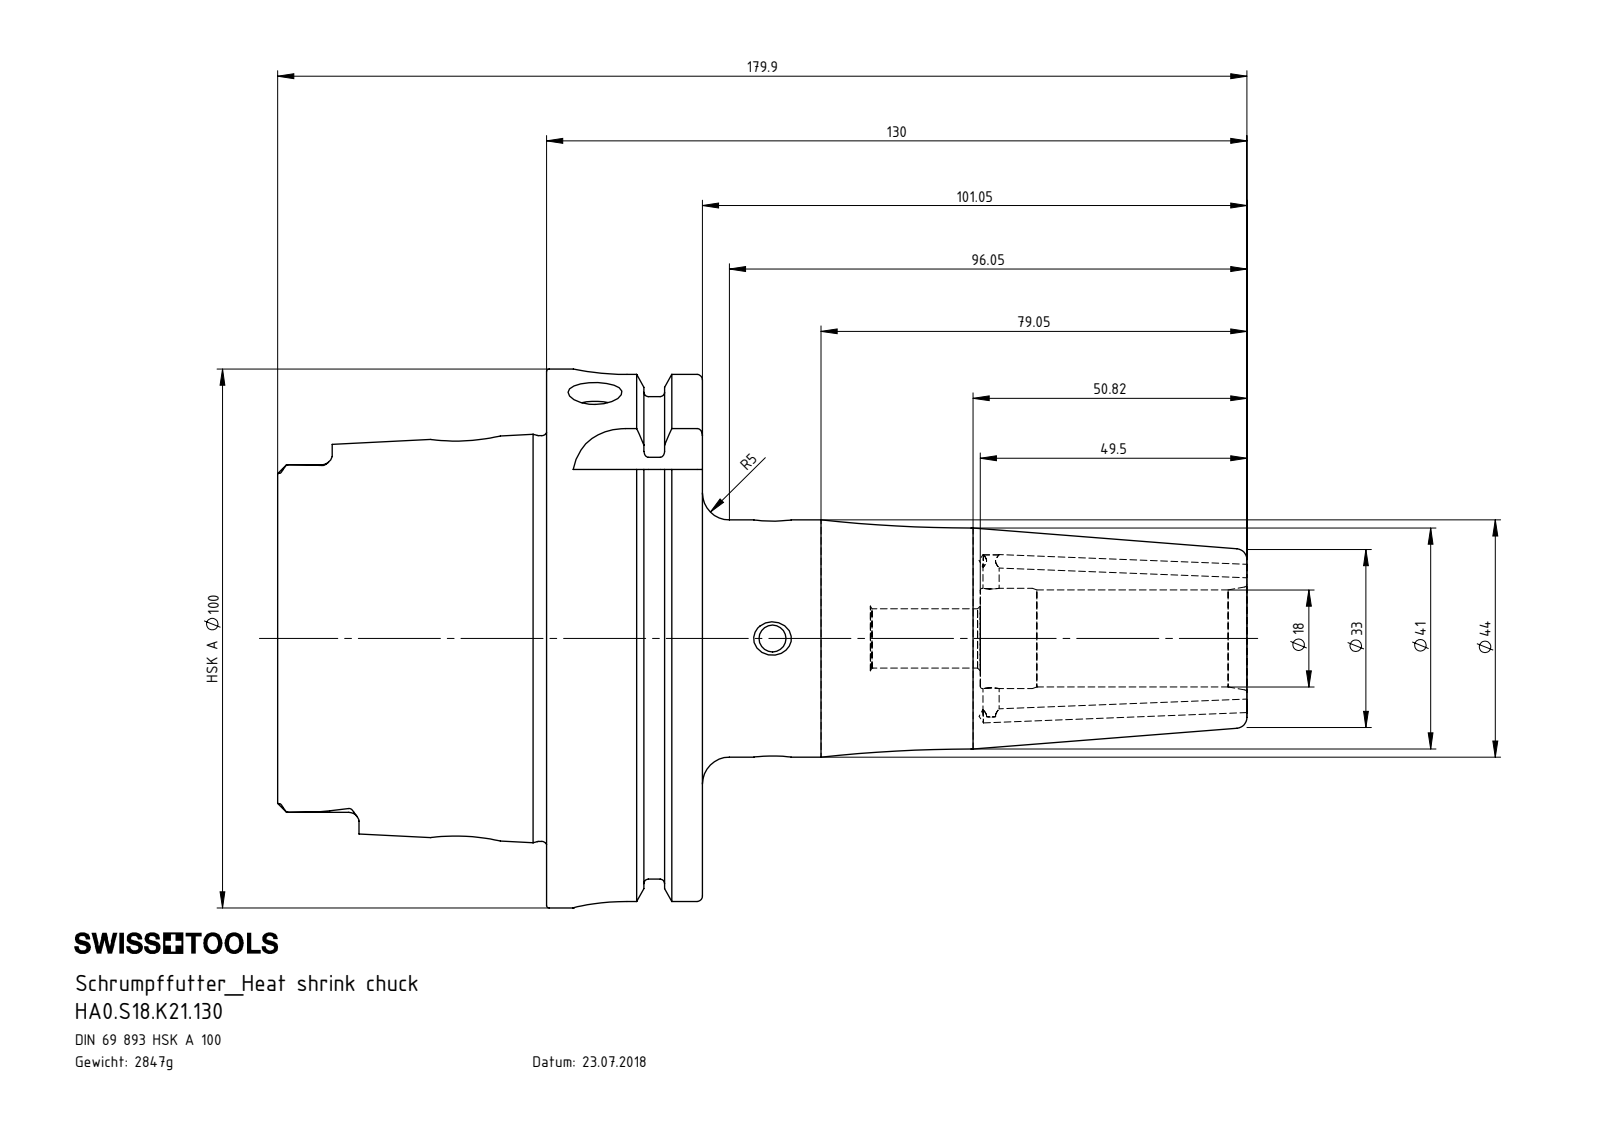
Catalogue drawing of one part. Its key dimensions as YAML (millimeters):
part_name: "HA0-S18.K21.130_C_Fertigbearbeitung; ERU-CJ2.001.006; ERU-AN5.K01.020_A; HA0.S18.K21.130"
step_written_by: "SolidWorks 2017 (CONFIG_CONTROL_DESIGN)"
units: millimeters
bodies: {solids: 4, faces: 305, planar: 95, cylindrical: 89, other: 121}
overall_size: [179.98, 100, 100]
volume: 362688
surface_area: 69034
round_holes:
  - {diameter: 10, count: 3}
  - {diameter: 2.5, count: 2}
  - {diameter: 5, count: 2}
  - {diameter: 12, count: 2}
  - {diameter: 3, count: 1}
  - {diameter: 6, count: 1}
  - {diameter: 11, count: 1}
  - {diameter: 18, count: 1}
  - {diameter: 18.6, count: 1}
  - {diameter: 22.5, count: 1}
  - {diameter: 26, count: 1}
  - {diameter: 53, count: 1}
round_bosses_or_shafts:
  - {diameter: 3, count: 2}
  - {diameter: 100, count: 1}
  - {diameter: 91.95, count: 1}
  - {diameter: 75.26, count: 1}
  - {diameter: 44, count: 1}
  - {diameter: 41, count: 1}
partial_cylinders:
  - {radius: 1.9, count: 6}
  - {radius: 4.88, count: 4}
  - {radius: 10, count: 4}
face_to_face_distances: [28.95, 12.45, 16.5, 49.9, 62.35, 78.85, 87.8, 15.85, 78.2, 28.3]
hole_center_spacings: [34.95, 40.55, 56.95, 97.5]
